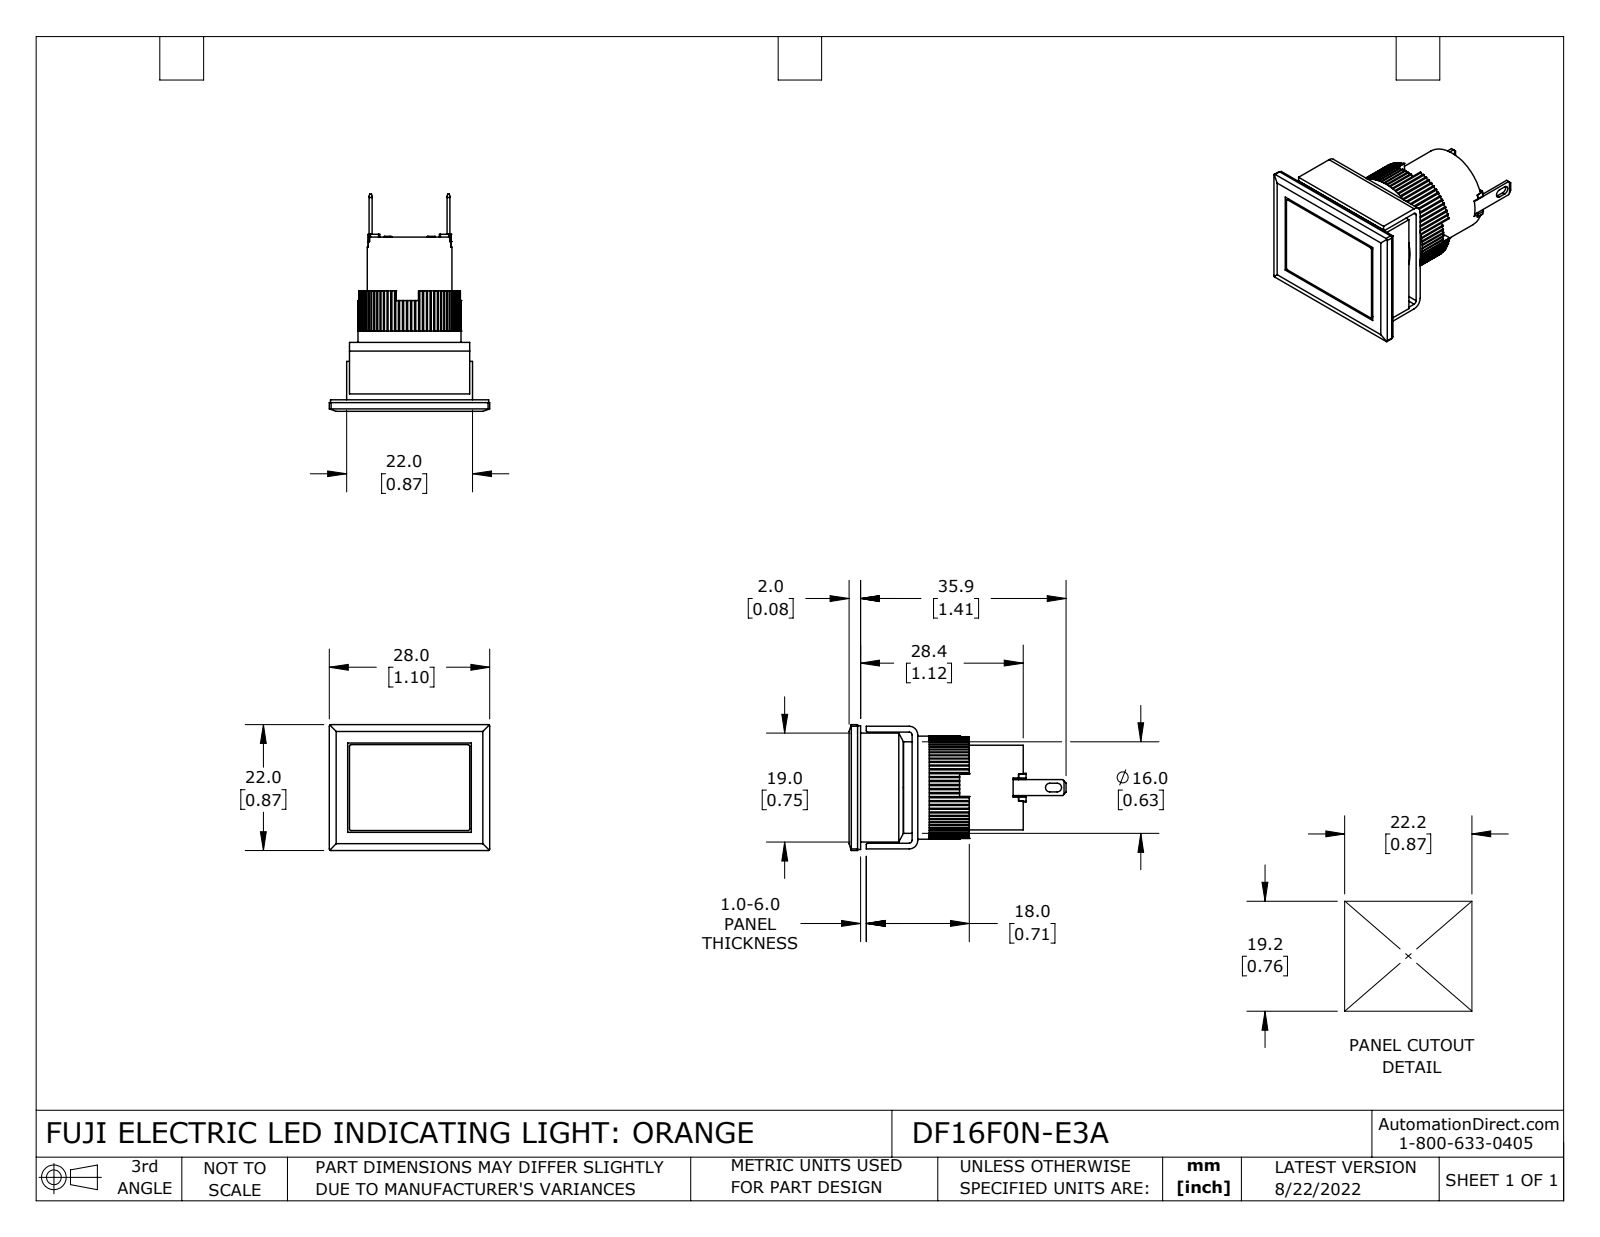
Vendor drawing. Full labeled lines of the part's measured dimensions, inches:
Part name (STEP PRODUCT): DF16F0N-E3A
STEP written by: SolidWorks 2021 (CONFIG_CONTROL_DESIGN)
Units: inches
Bodies: 10 solids, 495 faces (312 planar, 181 cylindrical, 2 other)
Overall size (bounding box): 1.492 × 1.102 × 0.866
Volume: 0.546 in³ · Surface area: 11.68 in²
Round holes (diameter × count): ⌀0.039 ×1, ⌀0.709 ×1
Round bosses / shafts (diameter × count): ⌀0.63 ×1, ⌀0.583 ×1
Partial cylindrical surfaces — rounded edges, fillets, slot ends (radius × count): R0.01 ×80, R0.008 ×12, R0.012 ×8, R0.02 ×2, R0.03 ×2, R0.059 ×2
Main face-to-face distances: 0.059, 0.374, 0.142, 0.02, 0.039, 0.315, 0.232, 0.083, 0.079, 0.756
